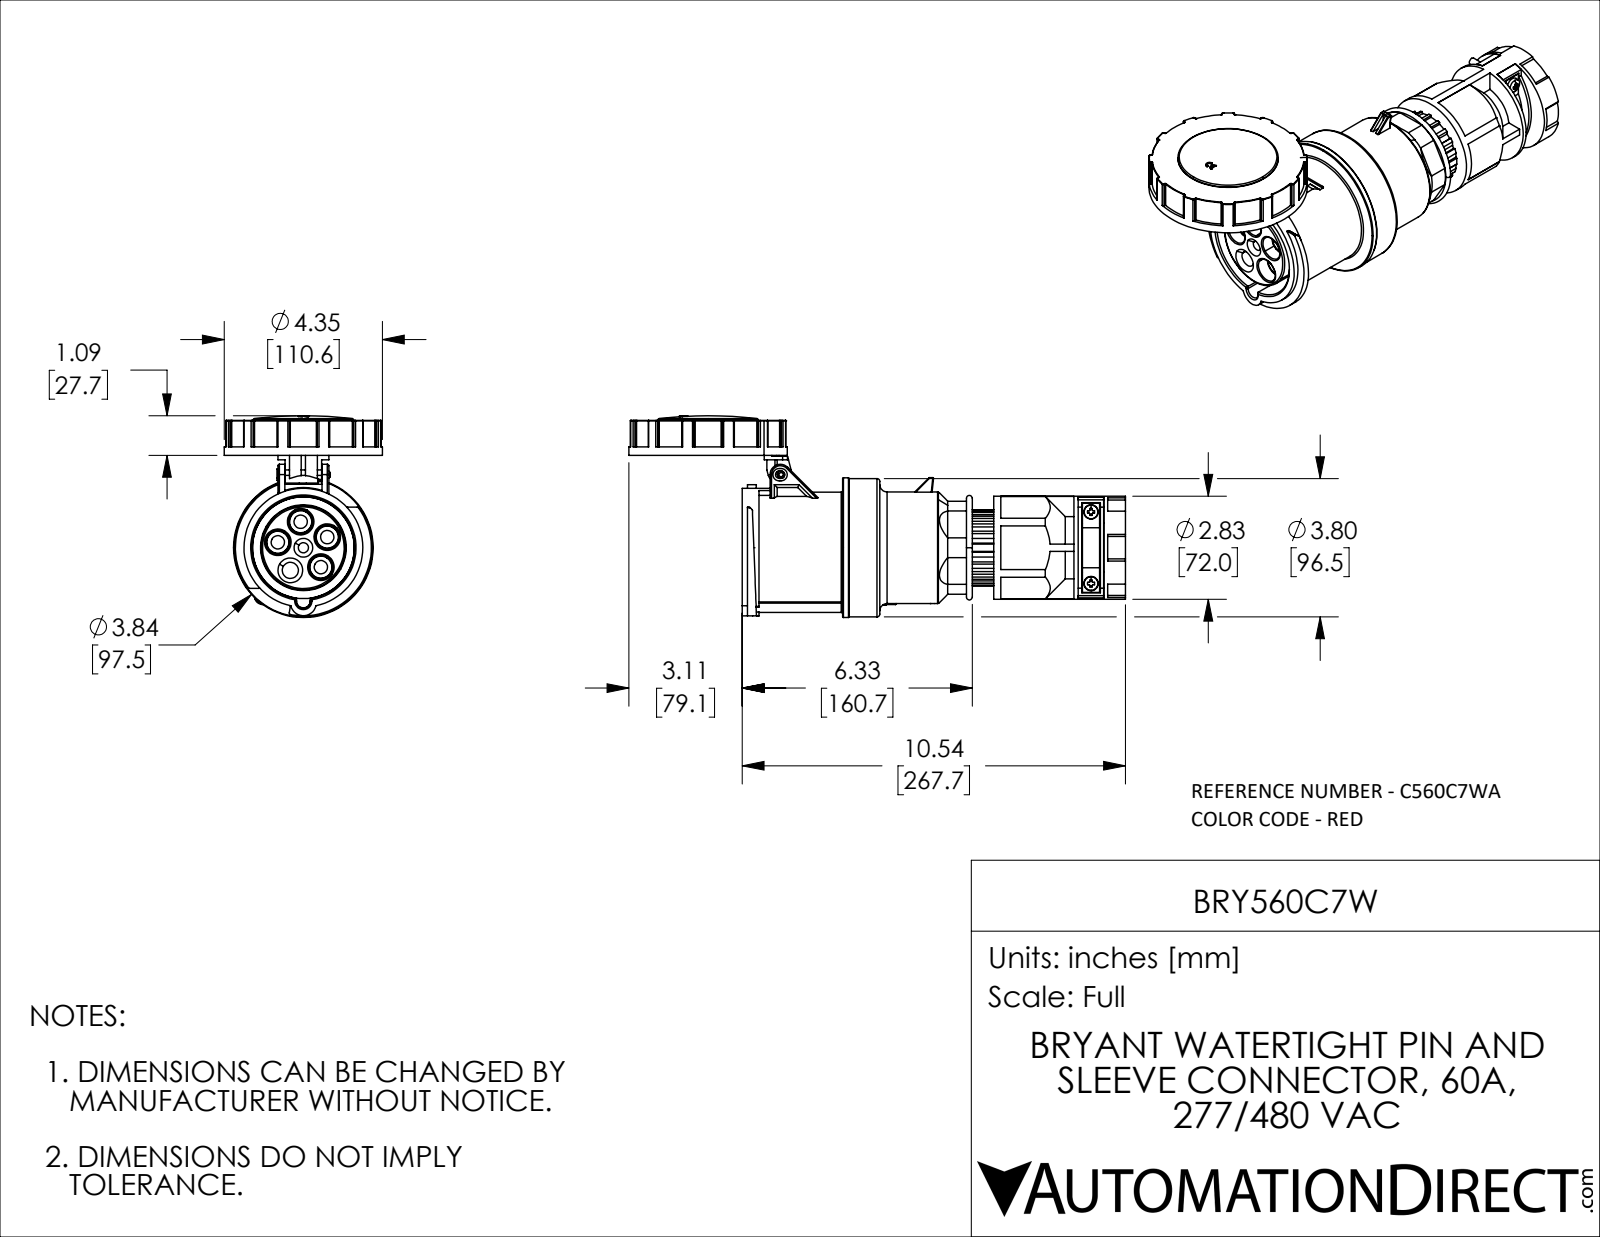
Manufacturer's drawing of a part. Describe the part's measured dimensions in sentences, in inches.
The part is named "BRY560C7W". Its 3-D file was written by "SolidWorks 2021 (CONFIG_CONTROL_DESIGN)". It is 9 solids with 1187 faces: 484 planar, 411 cylindrical and 292 other. Overall it measures 13.652 by 5.547 by 4.352 inches. Its volume is 70.36 cubic inches and its surface area 298.1 square inches. Round holes: 4 of diameter 0.366, 2 of diameter 0.197, 1 of diameter 0.28, 1 of diameter 0.445, 1 of diameter 1.457, 1 of diameter 2.579, 1 of diameter 3.961. Round bosses or shafts: 1 of diameter 4.352, 1 of diameter 3.839, 1 of diameter 3.799, 1 of diameter 3.268, 1 of diameter 3.071, 1 of diameter 3.055, 1 of diameter 2.835, 1 of diameter 2.795. Partial cylindrical surfaces (rounded edges, fillets, slot ends): 48 of radius 0.012, 40 of radius 0.039, 15 of radius 0.02, 6 of radius 1.358, 4 of radius 0.016, 4 of radius 0.079, 2 of radius 0.069, 2 of radius 0.098. The main face-to-face distances are 0.846, 0.118, 2.913, 2.559, 1.024, 0.197, 0.61, 3.622, 0.591, 0.728. The hole center spacings are 0.719, 0.844, 1.367, 0.718, 0.845, 1.366, 1.969.
